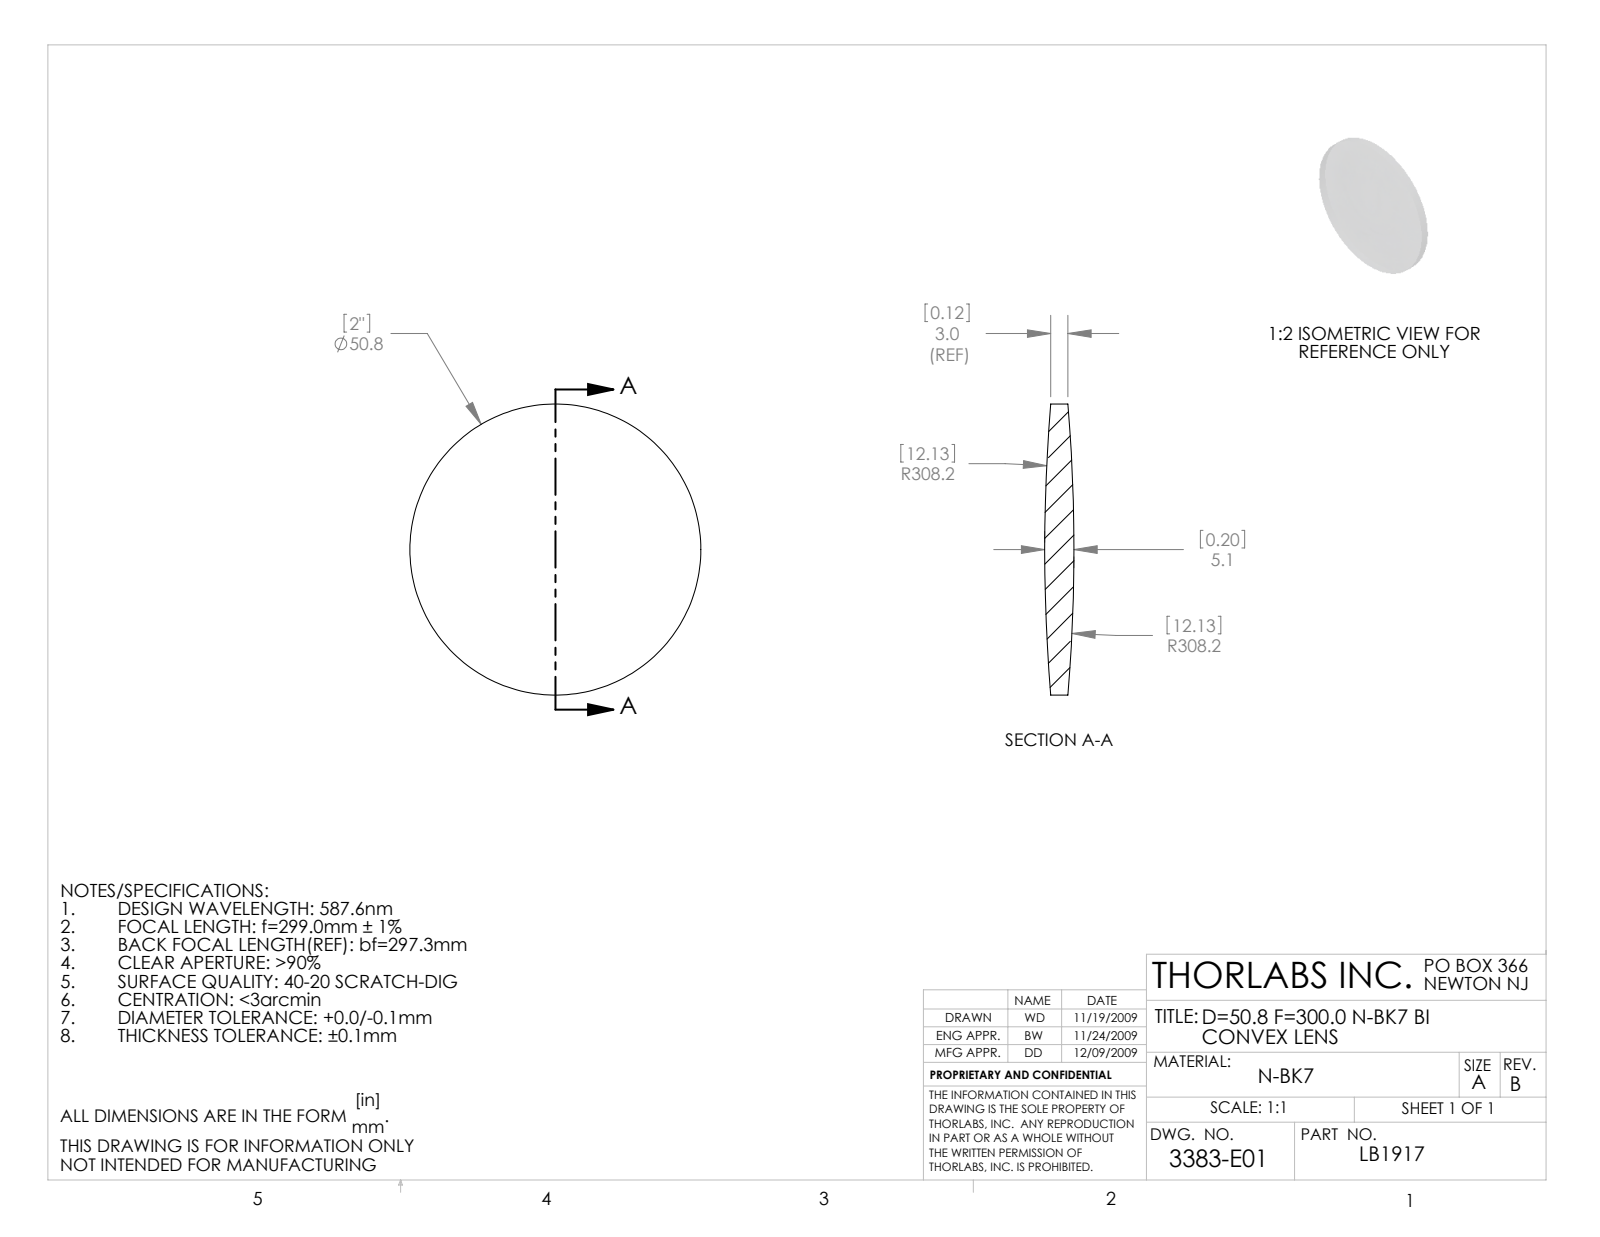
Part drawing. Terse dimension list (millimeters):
name: 3383-E0W
written by: SolidWorks 2009 (AUTOMOTIVE_DESIGN)
unit: mm
bodies: 1 solid, 6 faces (0 planar, 2 cylindrical, 4 other)
size: 50.8 × 50.8 × 5.1
volume: 8 213 mm³; area: 4 540 mm²
bosses: 1× ⌀50.8
